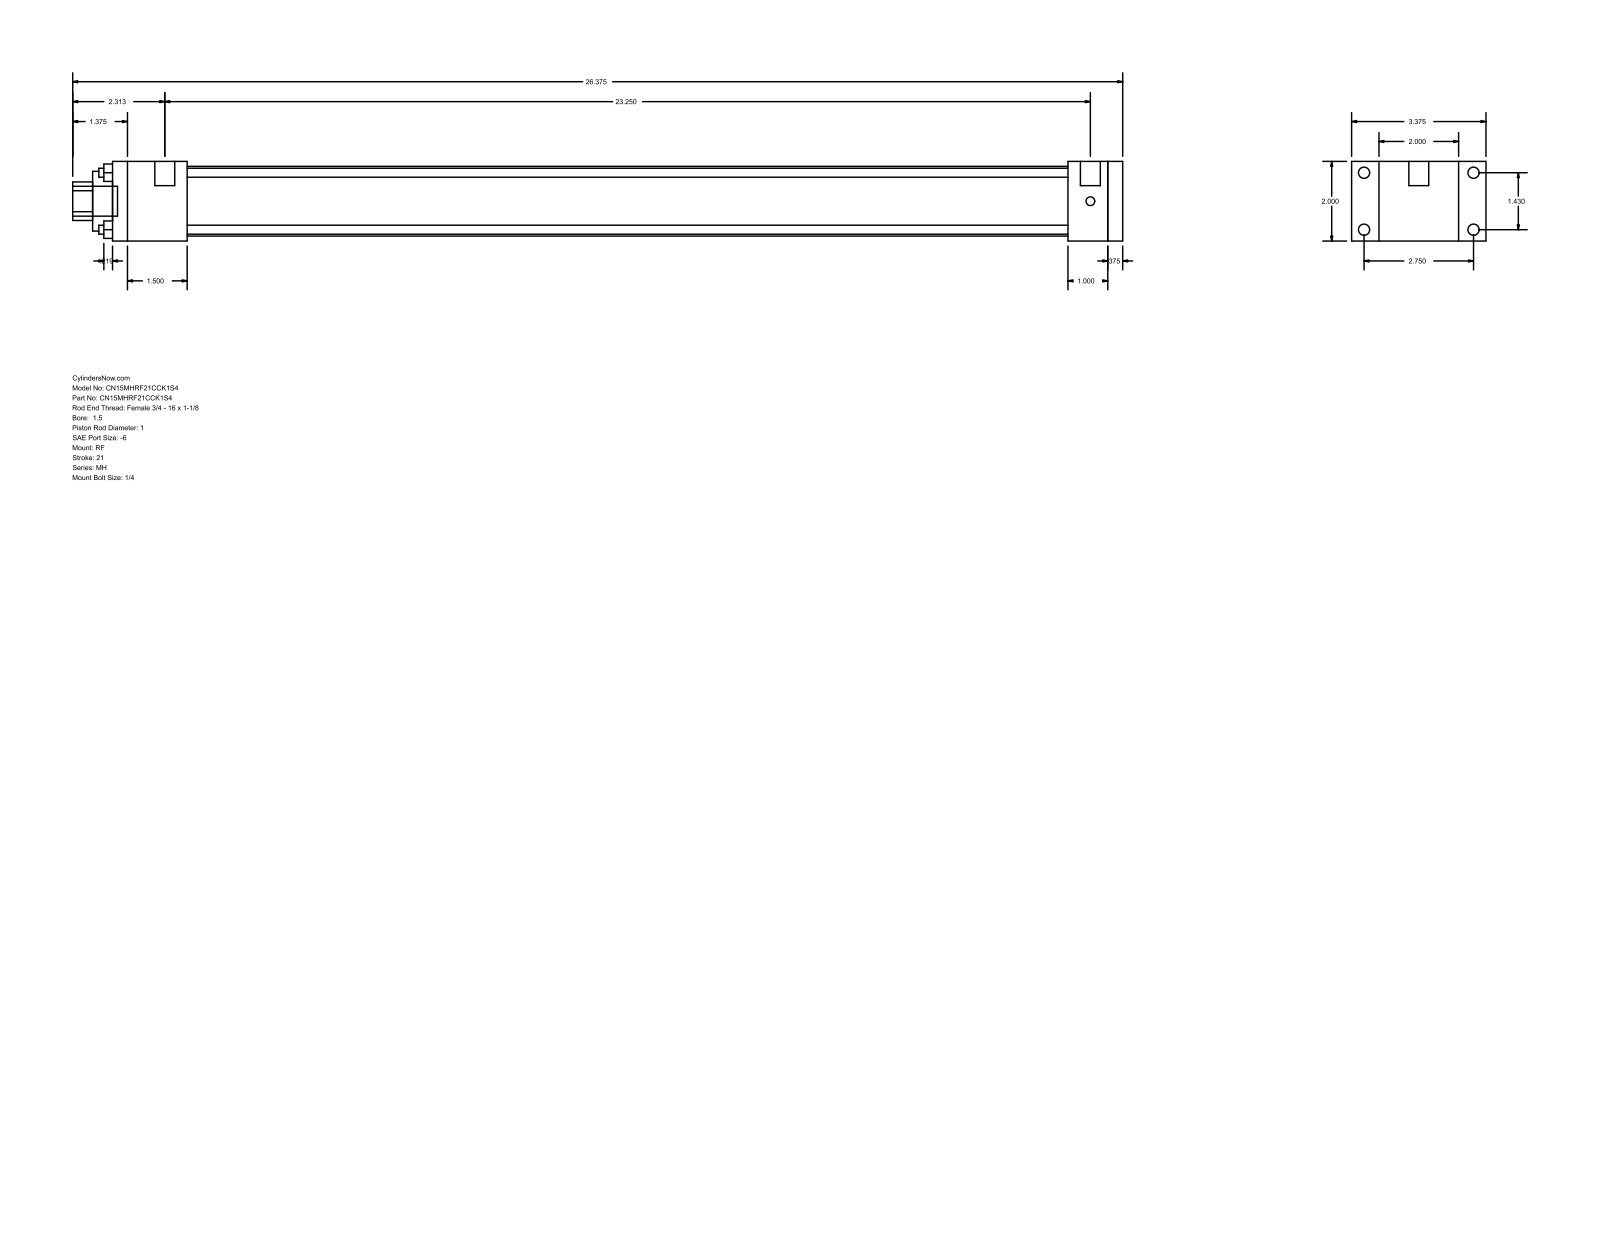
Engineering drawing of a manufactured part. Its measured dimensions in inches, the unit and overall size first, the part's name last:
Units: inches
Overall size (bounding box): 26.375 × 3.375 × 2
Round holes (diameter × count): ⌀0.225 ×4, ⌀1 ×1, ⌀1.5 ×1, ⌀1.75 ×1
Round bosses / shafts (diameter × count): ⌀0.281 ×4, ⌀0.219 ×4, ⌀0.5 ×2, ⌀0.75 ×1
Partial cylindrical surfaces — rounded edges, fillets, slot ends (radius × count): R0.484 ×1
Main face-to-face distances: 2, 0.375, 25, 1, 25.375, 0.687, 2.687, 24, 1.375, 1.875
Hole centre spacings: 1.011, 1.43, 2.022
Bodies: 0 solids, 92 faces (64 planar, 28 cylindrical, 0 other)
Part name (STEP PRODUCT): MH_RF__0150_1
STEP written by: GSSL Pune (CONFIG_CONTROL_DESIGN)
